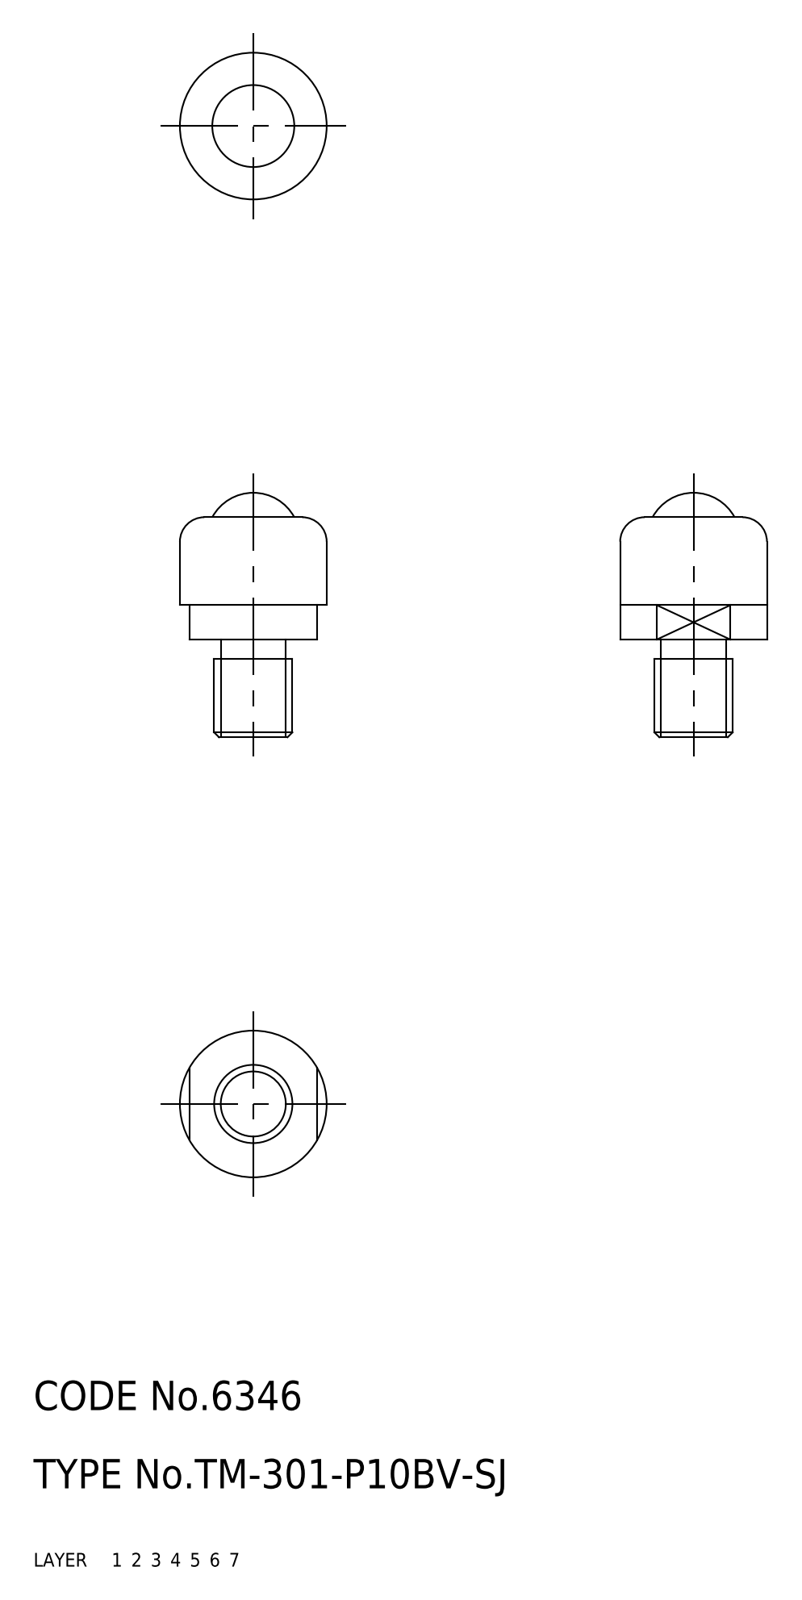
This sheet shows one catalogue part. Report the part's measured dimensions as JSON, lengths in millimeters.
{"part_name": "67111055; 67111068; 67111081", "step_written_by": "CADfix (AUTOMOTIVE_DESIGN)", "units": "millimeters", "bodies": {"solids": 3, "faces": 29, "planar": 0, "cylindrical": 0, "other": 29}, "overall_size": [25, 15, 15], "volume_mm3": 1815, "surface_area_mm2": 1985}
